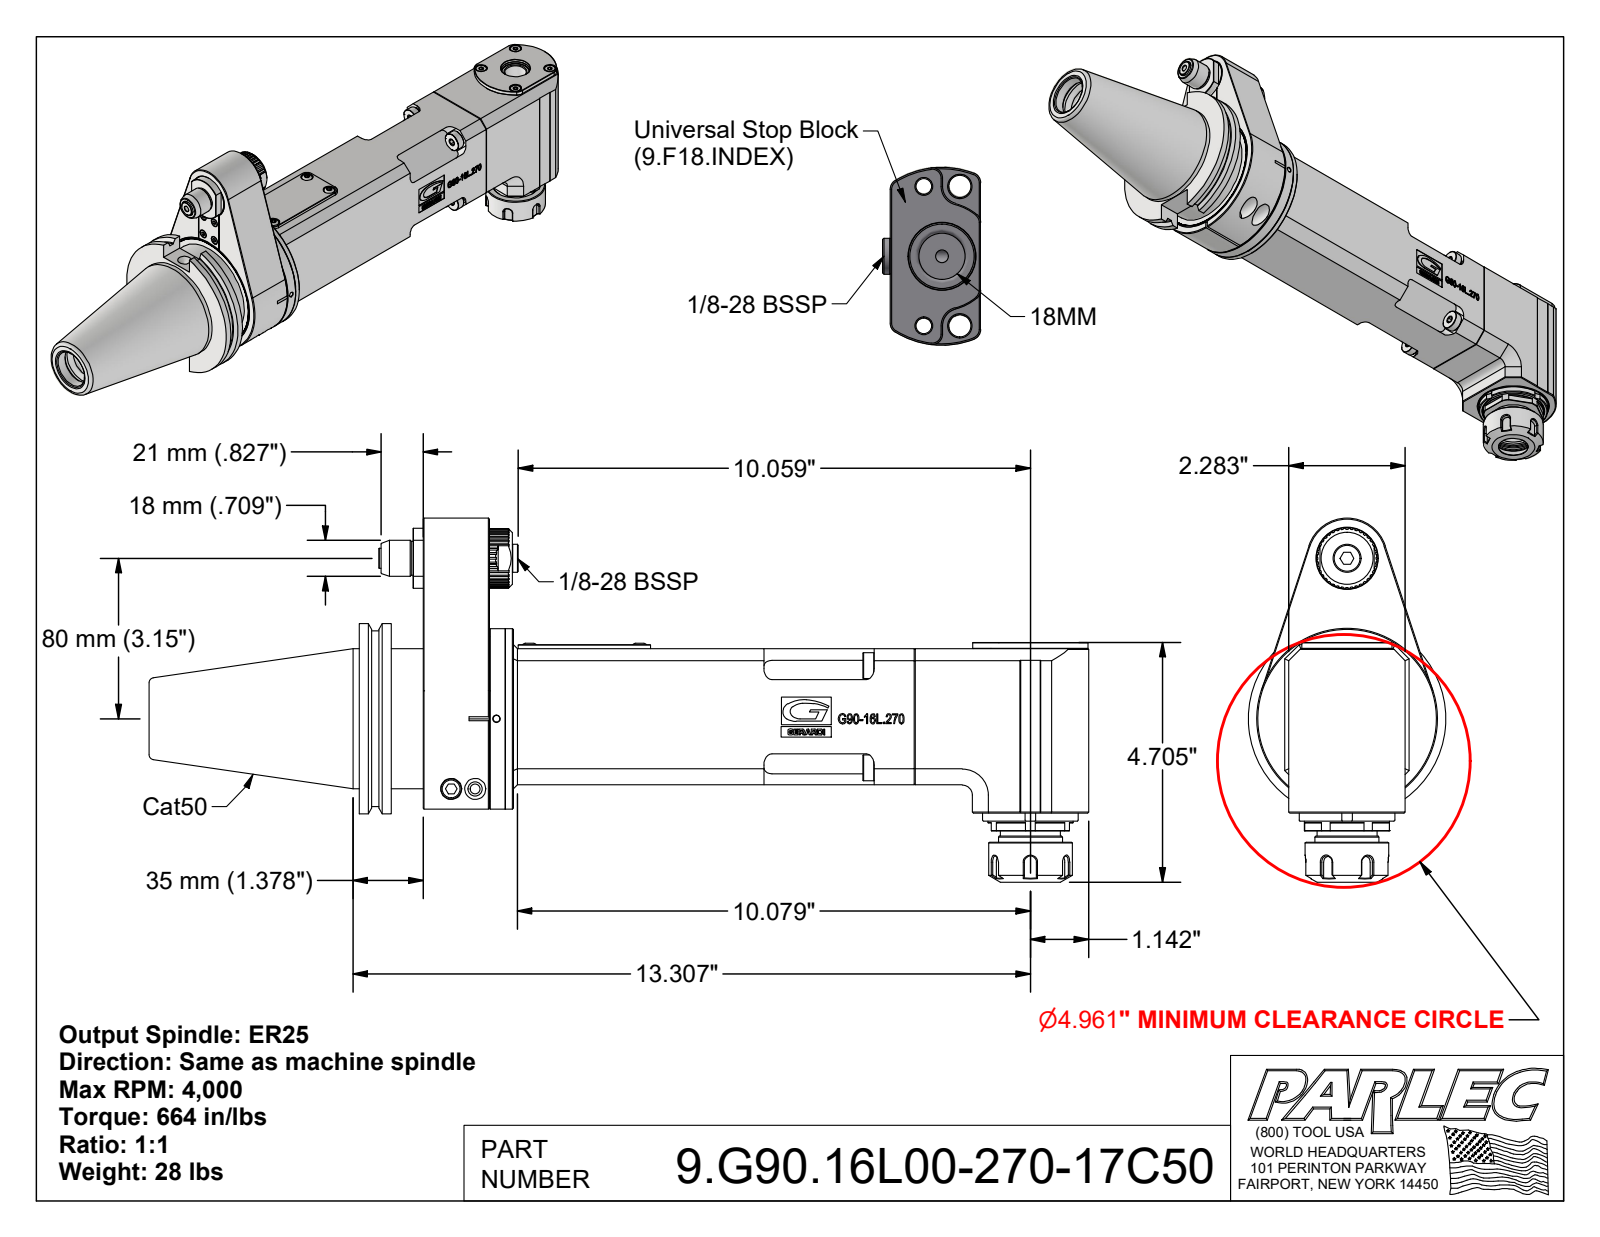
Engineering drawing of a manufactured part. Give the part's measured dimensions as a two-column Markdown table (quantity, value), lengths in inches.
| quantity | value |
| --- | --- |
| part name | 9.G90.16L00-270-17C50; 9_GA1_458_1 (Classic, Type 1, Cat50, 80mm); G90-16L-270 |
| STEP written by | Autodesk Inventor 2022 (AUTOMOTIVE_DESIGN) |
| units | inches |
| bodies | 21 solids, 1501 faces (752 planar, 268 cylindrical, 481 other) |
| overall size | 18.457 × 7.146 × 3.875 |
| volume | 87.69 in³ |
| surface area | 438.1 in² |
| round holes (diameter × count) | 0.197 × 7, 0.335 × 7, 0.13 × 6, 0.236 × 5, 0.315 × 5, 0.165 × 4, 0.157 × 3, 0.276 × 2, 0.413 × 2, 0.709 × 2, 1.201 × 2, 1.654 × 2 |
| round bosses / shafts (diameter × count) | 0.512 × 4, 0.307 × 4, 0.299 × 4, 0.394 × 3, 3.875 × 1, 3.593 × 1, 3.543 × 1, 3.228 × 1 |
| partial cylindrical surfaces (radius × count) | 0.157 × 16, 0.118 × 8, 0.098 × 5, 0.197 × 5, 0.236 × 4, 0.085 × 2, 0.151 × 2, 0.079 × 1 |
| main face-to-face distances | 2.283, 2.677, 1.299, 0.626, 0.315, 0.039, 0.354, 2.551, 1.925, 1.252 |
| hole center spacings | 0.678, 1.39, 1.476, 2.557, 0.551, 0.78, 0.945, 1.336 |
